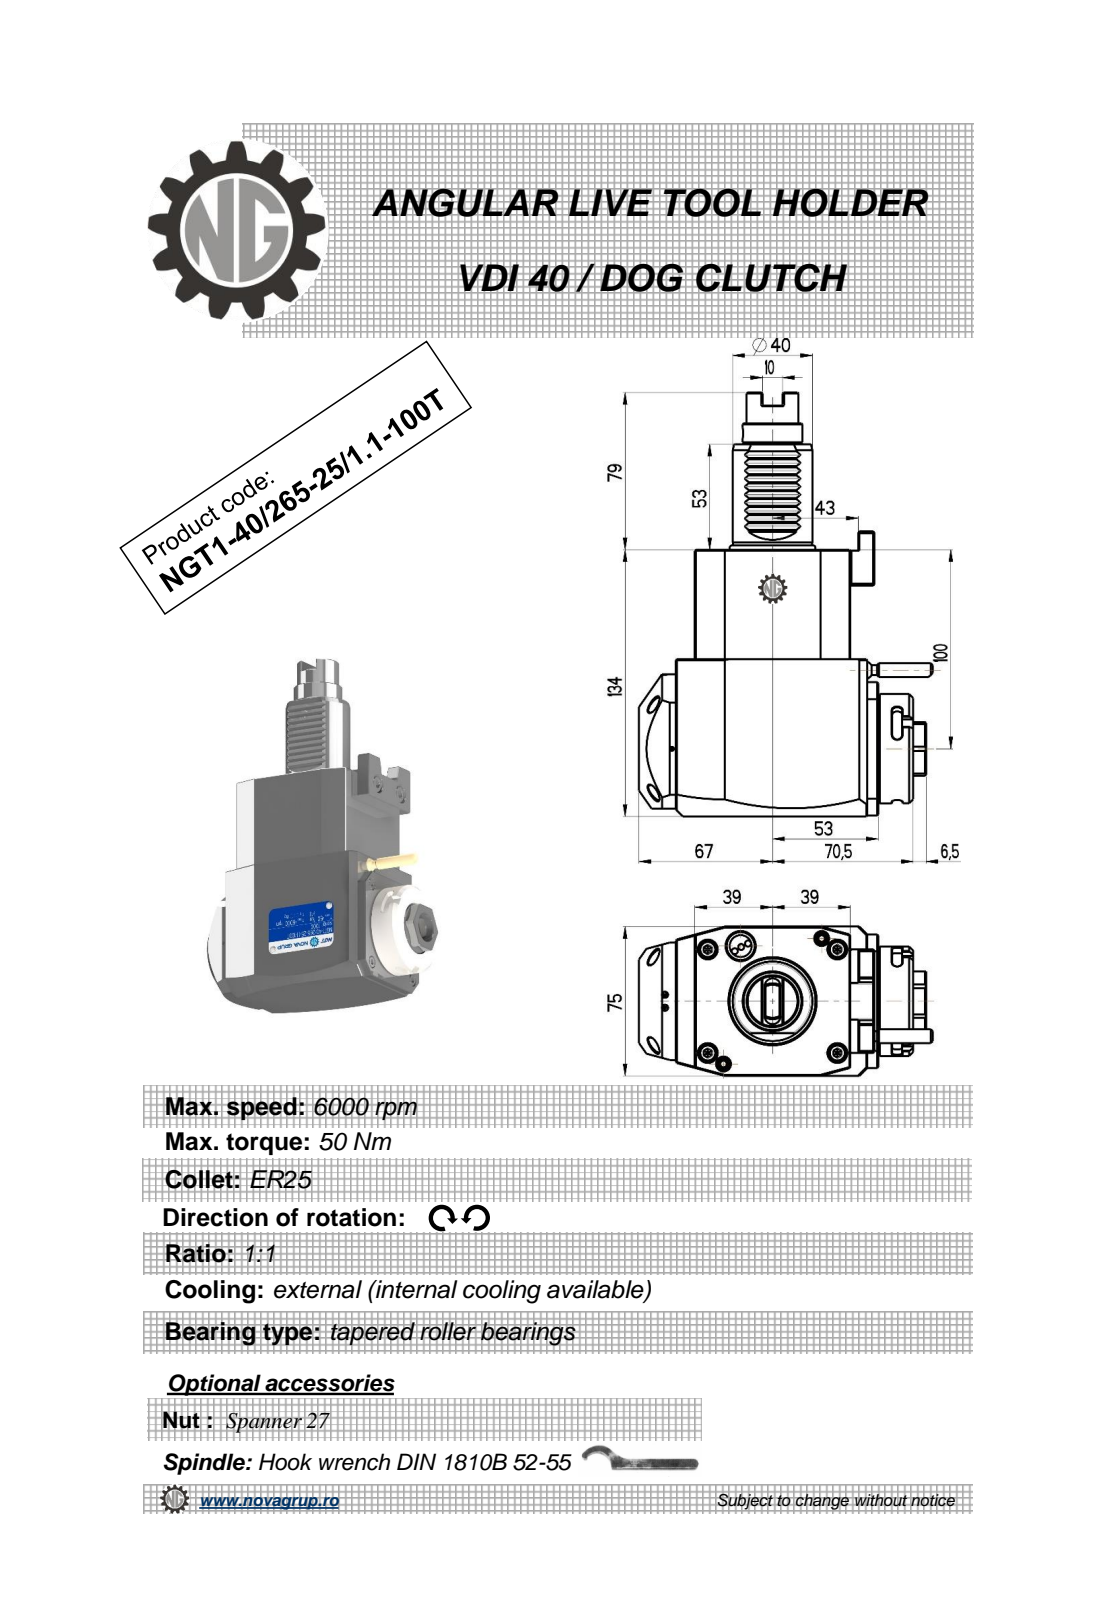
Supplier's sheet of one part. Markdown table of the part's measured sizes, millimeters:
| quantity | value |
| --- | --- |
| part name | NGT1_40_265_25_1_1_100T |
| STEP written by | PRO/ENGINEER BY PARAMETRIC TECHNOLOGY CORPORATION, 2010280 (CONFIG_CONTROL_DESIGN) |
| units | millimeters |
| bodies | 1 solid, 335 faces (204 planar, 69 cylindrical, 62 other) |
| overall size | 213 × 147.33 × 75 |
| volume | 1 077 000 mm³ |
| surface area | 77 027 mm² |
| round holes (diameter × count) | 2.5 × 1, 3 × 1, 4.2 × 1, 18 × 1 |
| round bosses / shafts (diameter × count) | 55 × 1, 48 × 1, 40 × 1, 30 × 1, 26 × 1, 8 × 1, 7 × 1, 5 × 1 |
| partial cylindrical surfaces (radius × count) | 0.3 × 10, 0.26 × 6, 2.5 × 6, 0.5 × 3, 1 × 2, 180 × 2, 12.5 × 1, 15 × 1 |
| main face-to-face distances | 75, 134, 78, 14, 92, 17.5, 31.5, 84.88, 109.5, 4 |
| hole center spacings | 43.2, 120.28, 158.5 |
